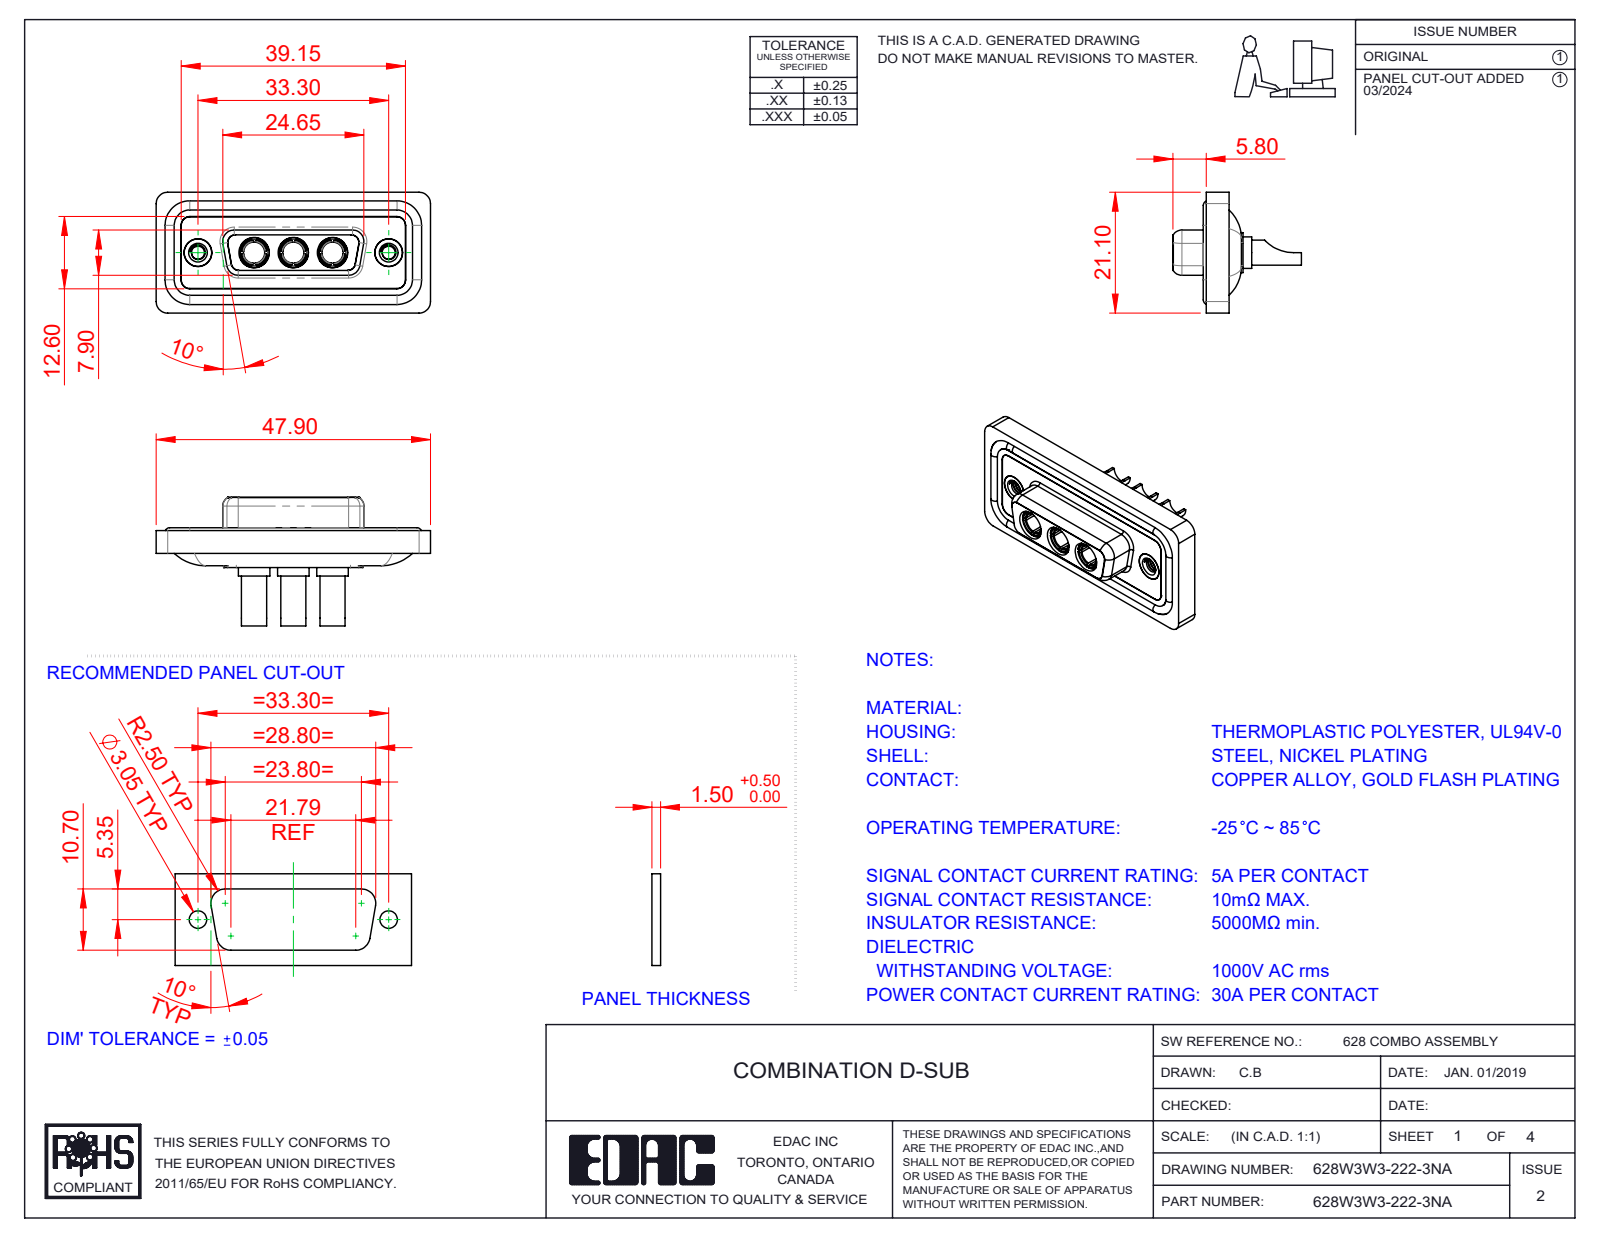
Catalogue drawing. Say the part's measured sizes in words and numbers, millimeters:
The part is named "628Combo Housing_3W3; Power Socket_30A SC; 628Combo Shell Front_15 Contacts; 628Combo Threaded Rivet_A (+3 more)". Its 3-D file was written by "SolidWorks 2023 (CONFIG_CONTROL_DESIGN)". It is 13 solids with 624 faces: 201 planar, 268 cylindrical and 155 other. Overall it measures 47.9 by 22.45 by 21.1 millimeters. Its volume is 6 100 cubic millimeters and its surface area 10 059 square millimeters. Round holes: 5 of diameter 4.85, 3 of diameter 3.5, 3 of diameter 3.7, 3 of diameter 5.3, 2 of diameter 2.26, 2 of diameter 4, 2 of diameter 4.05, 2 of diameter 5. Round bosses or shafts: 4 of diameter 1.6, 3 of diameter 5.5, 3 of diameter 5.2, 3 of diameter 4.96, 3 of diameter 4.75, 3 of diameter 4.4, 3 of diameter 3.75, 2 of diameter 4.95. Partial cylindrical surfaces (rounded edges, fillets, slot ends): 22 of radius 1.5, 20 of radius 2, 12 of radius 1.35, 8 of radius 1.6, 4 of radius 0.25, 4 of radius 0.5, 4 of radius 0.6, 4 of radius 0.65. The main face-to-face distances are 0.4, 1.8, 1.6, 0.5, 7.45, 1.1, 2.9, 5.65, 7.05, 6.6. The hole center spacings are 6.85, 9.8, 16.65, 23.5, 13.7, 33.3.
